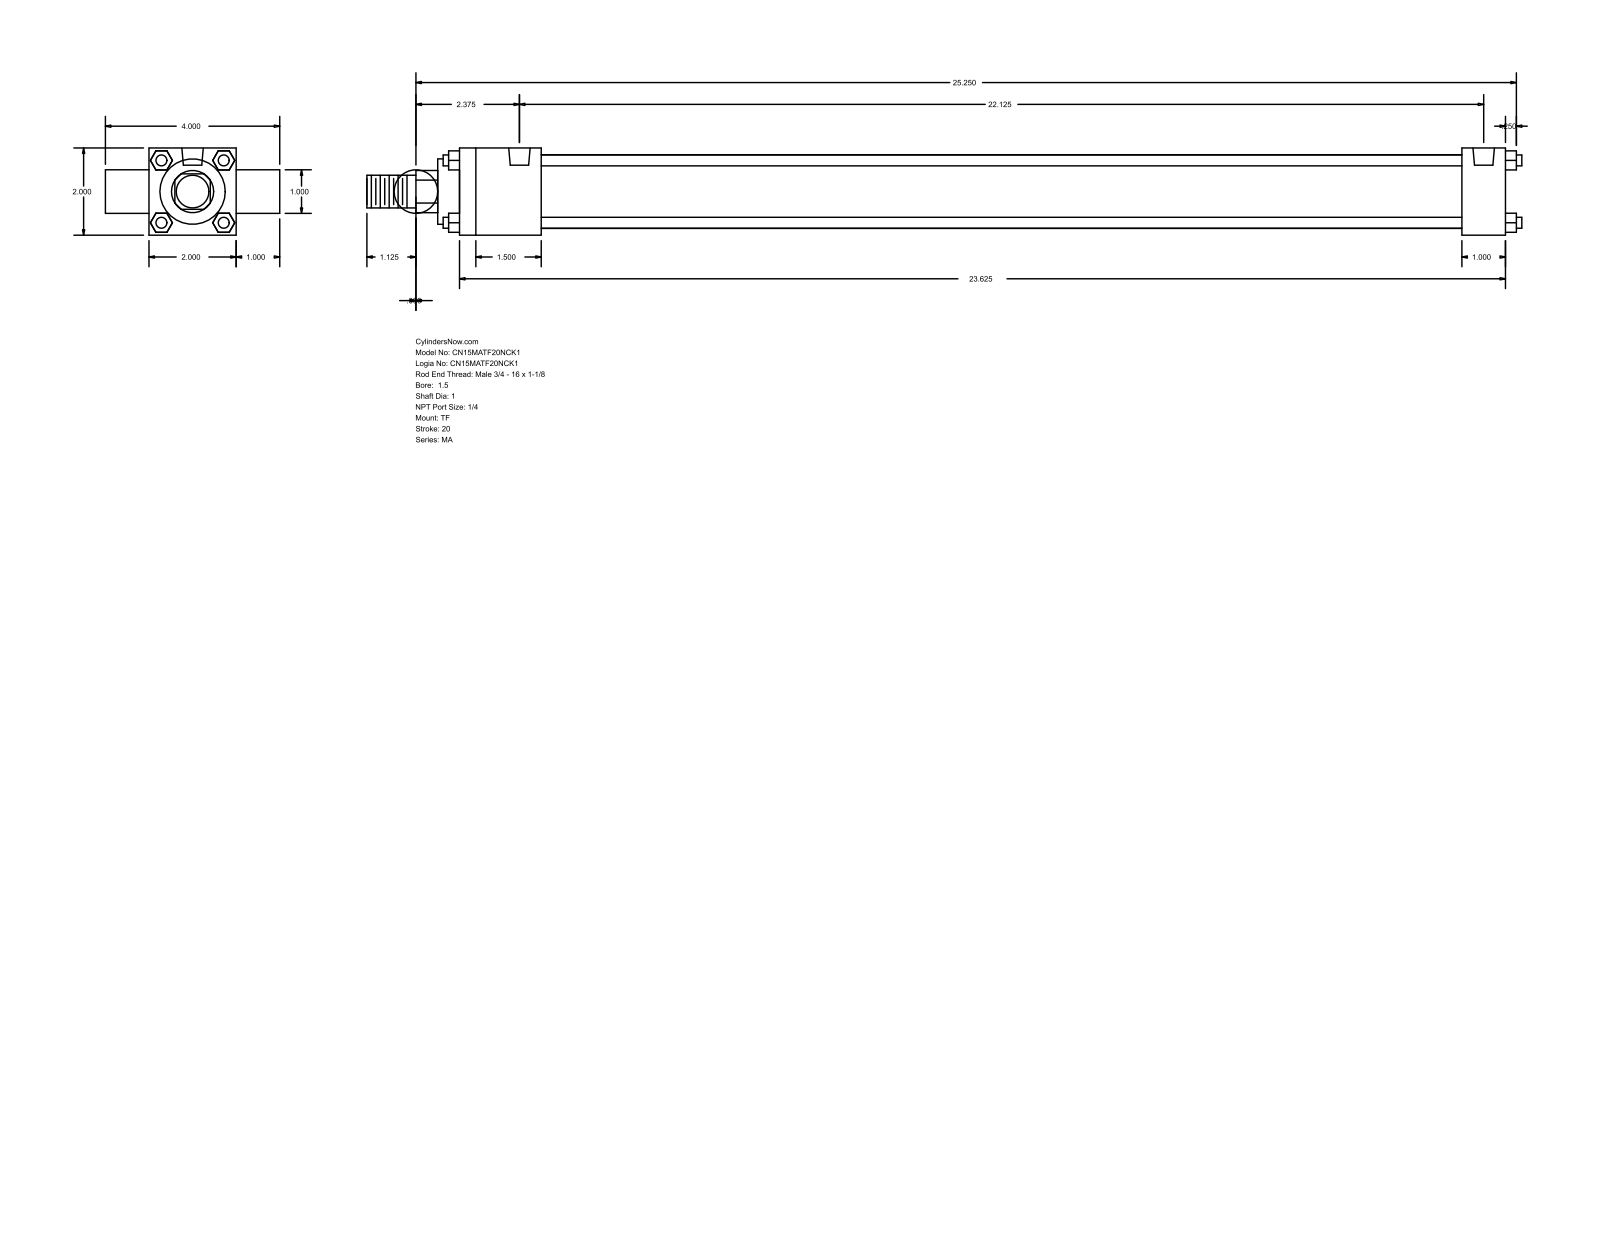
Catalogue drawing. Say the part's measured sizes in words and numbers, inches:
The part is named "MA_TF__0150_1". Its 3-D file was written by "GSSL Pune (CONFIG_CONTROL_DESIGN)". It is 0 solids with 120 faces: 92 planar, 28 cylindrical and 0 other. Overall it measures 26.5 by 4 by 2 inches. Round holes: 3 of diameter 0.313, 2 of diameter 0.492. Round bosses or shafts: 4 of diameter 0.25, 2 of diameter 1, 1 of diameter 1.69, 1 of diameter 1.5, 1 of diameter 0.75. Partial cylindrical surfaces (rounded edges, fillets, slot ends): 1 of radius 0.484. The main face-to-face distances are 2, 1, 24, 3, 0.25, 1.875, 23, 21.125, 22.125, 24.5. The hole center spacings are 22.125.
